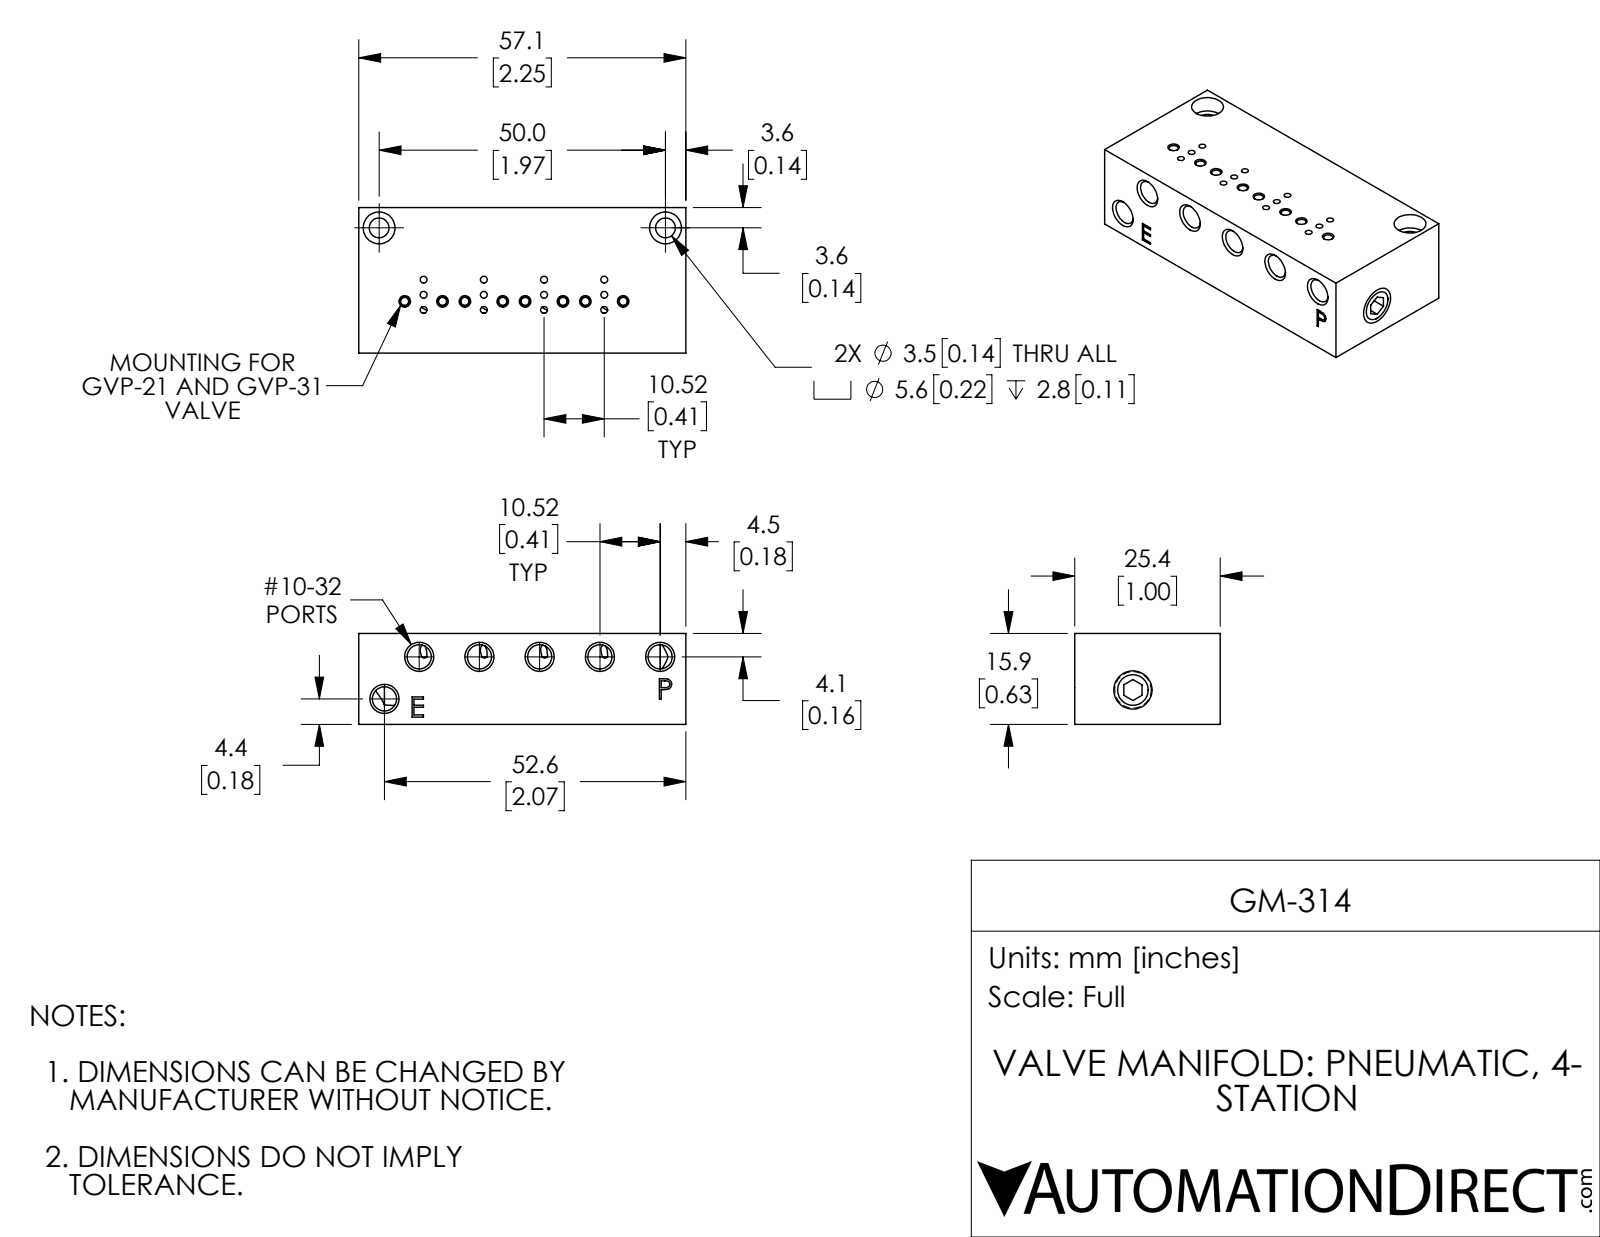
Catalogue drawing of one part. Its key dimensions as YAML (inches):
part_name: "GM-314"
step_written_by: "SolidWorks 2018 (AUTOMOTIVE_DESIGN)"
units: inches
bodies: {solids: 3, faces: 221, planar: 57, cylindrical: 84, other: 80}
overall_size: [2.249, 1, 0.625]
volume: 1.197
surface_area: 14.09
round_holes:
  - {diameter: 0.047, count: 12}
  - {diameter: 0.055, count: 8}
  - {diameter: 0.063, count: 8}
  - {diameter: 0.166, count: 6}
  - {diameter: 0.136, count: 2}
  - {diameter: 0.213, count: 2}
  - {diameter: 0.219, count: 2}
round_bosses_or_shafts:
  - {diameter: 0.25, count: 2}
face_to_face_distances: [0.625, 1, 2.249, 0.125, 0.513, 0.112, 0.25, 1.999, 0.16, 2.089]
hole_center_spacings: [0.828, 0.414, 0.104, 0.198, 0.414, 0.427, 0.835, 0.137]
